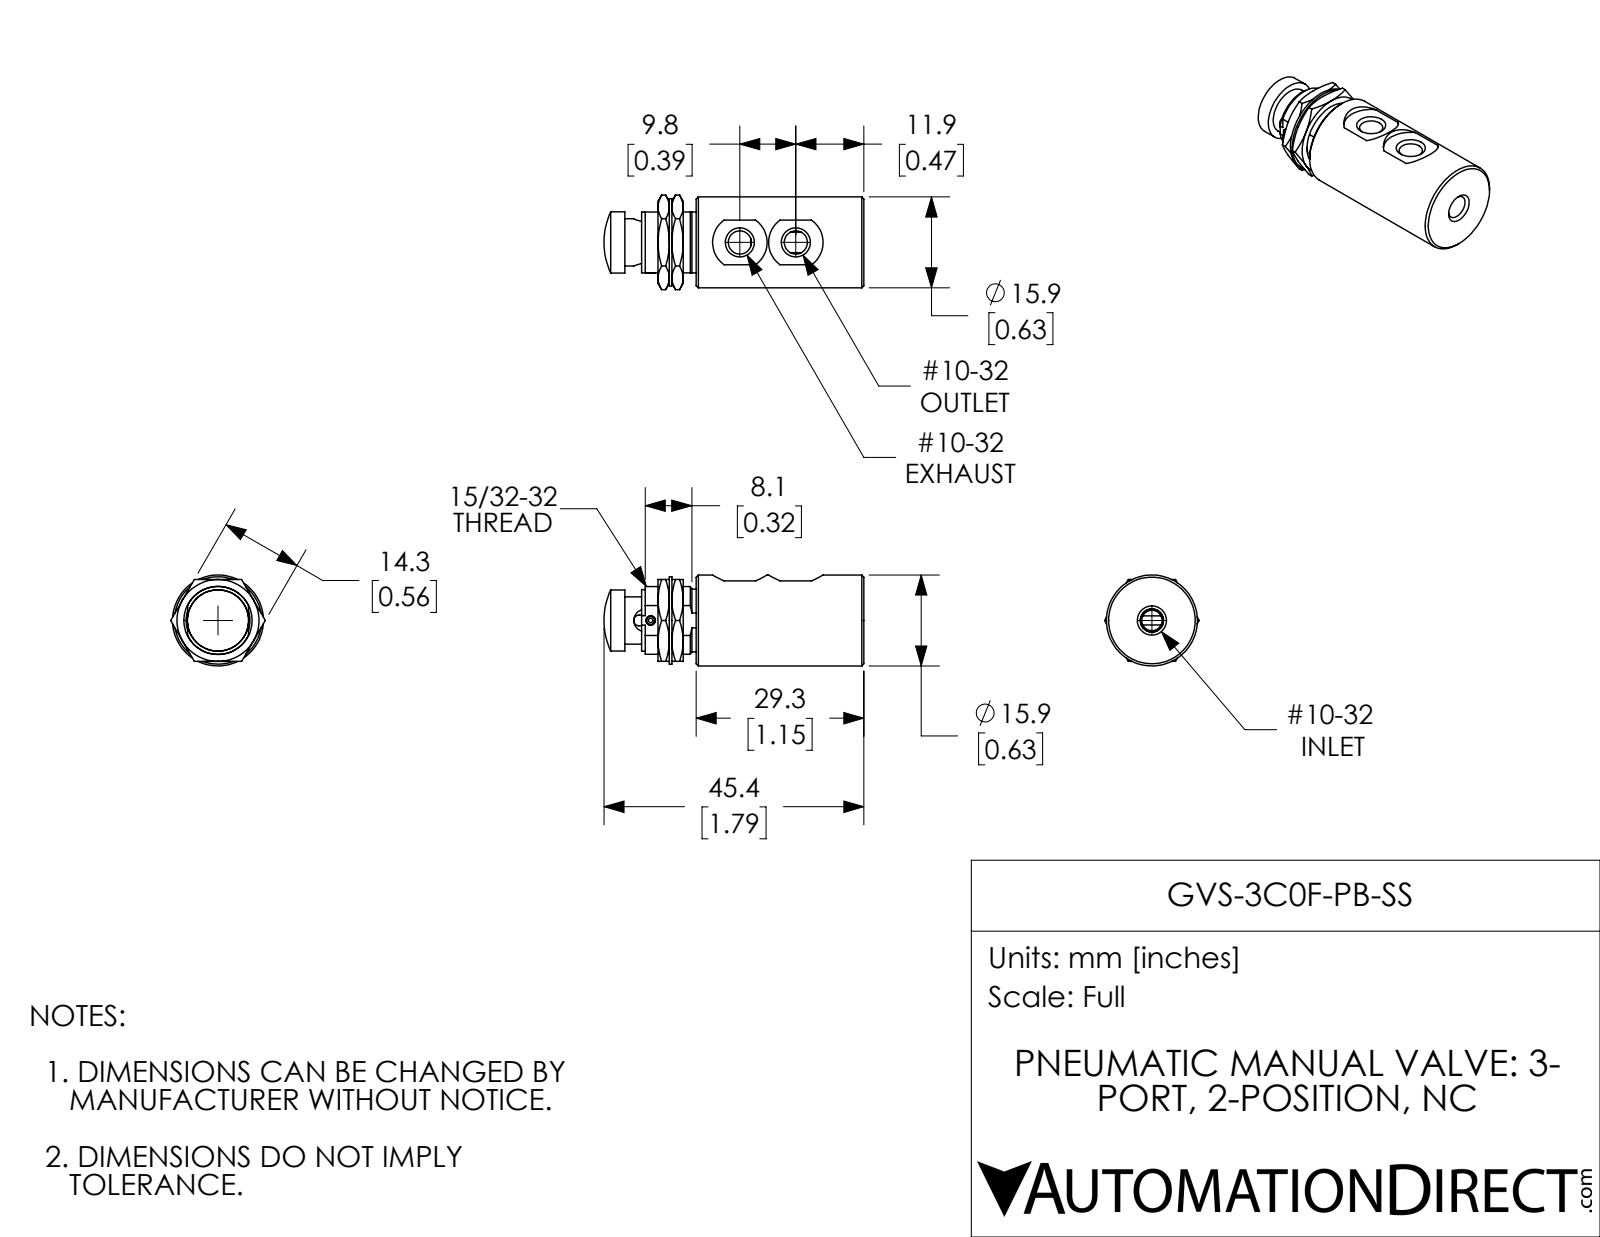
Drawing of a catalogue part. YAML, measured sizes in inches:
part_name: "GVS-3C0F-PB-SS"
step_written_by: "SolidWorks 2018 (AUTOMOTIVE_DESIGN)"
units: inches
bodies: {solids: 6, faces: 274, planar: 98, cylindrical: 103, other: 73}
overall_size: [1.787, 0.65, 0.625]
volume: 0.386
surface_area: 6.755
round_holes:
  - {diameter: 0.159, count: 3}
  - {diameter: 0.03, count: 1}
  - {diameter: 0.064, count: 1}
  - {diameter: 0.14, count: 1}
  - {diameter: 0.153, count: 1}
  - {diameter: 0.182, count: 1}
  - {diameter: 0.198, count: 1}
  - {diameter: 0.229, count: 1}
  - {diameter: 0.34, count: 1}
  - {diameter: 0.438, count: 1}
round_bosses_or_shafts:
  - {diameter: 0.625, count: 1}
  - {diameter: 0.6, count: 1}
  - {diameter: 0.43, count: 1}
  - {diameter: 0.423, count: 1}
  - {diameter: 0.42, count: 1}
  - {diameter: 0.325, count: 1}
  - {diameter: 0.063, count: 1}
partial_cylinders:
  - {radius: 0.037, count: 2}
  - {radius: 0.188, count: 2}
  - {radius: 0.233, count: 1}
  - {radius: 0.239, count: 1}
  - {radius: 0.26, count: 1}
face_to_face_distances: [1.337, 1.32, 0.017, 0.078, 0.095, 1.153, 0.168, 0.185, 0.563, 1.415]
hole_center_spacings: [0.039, 0.385]
